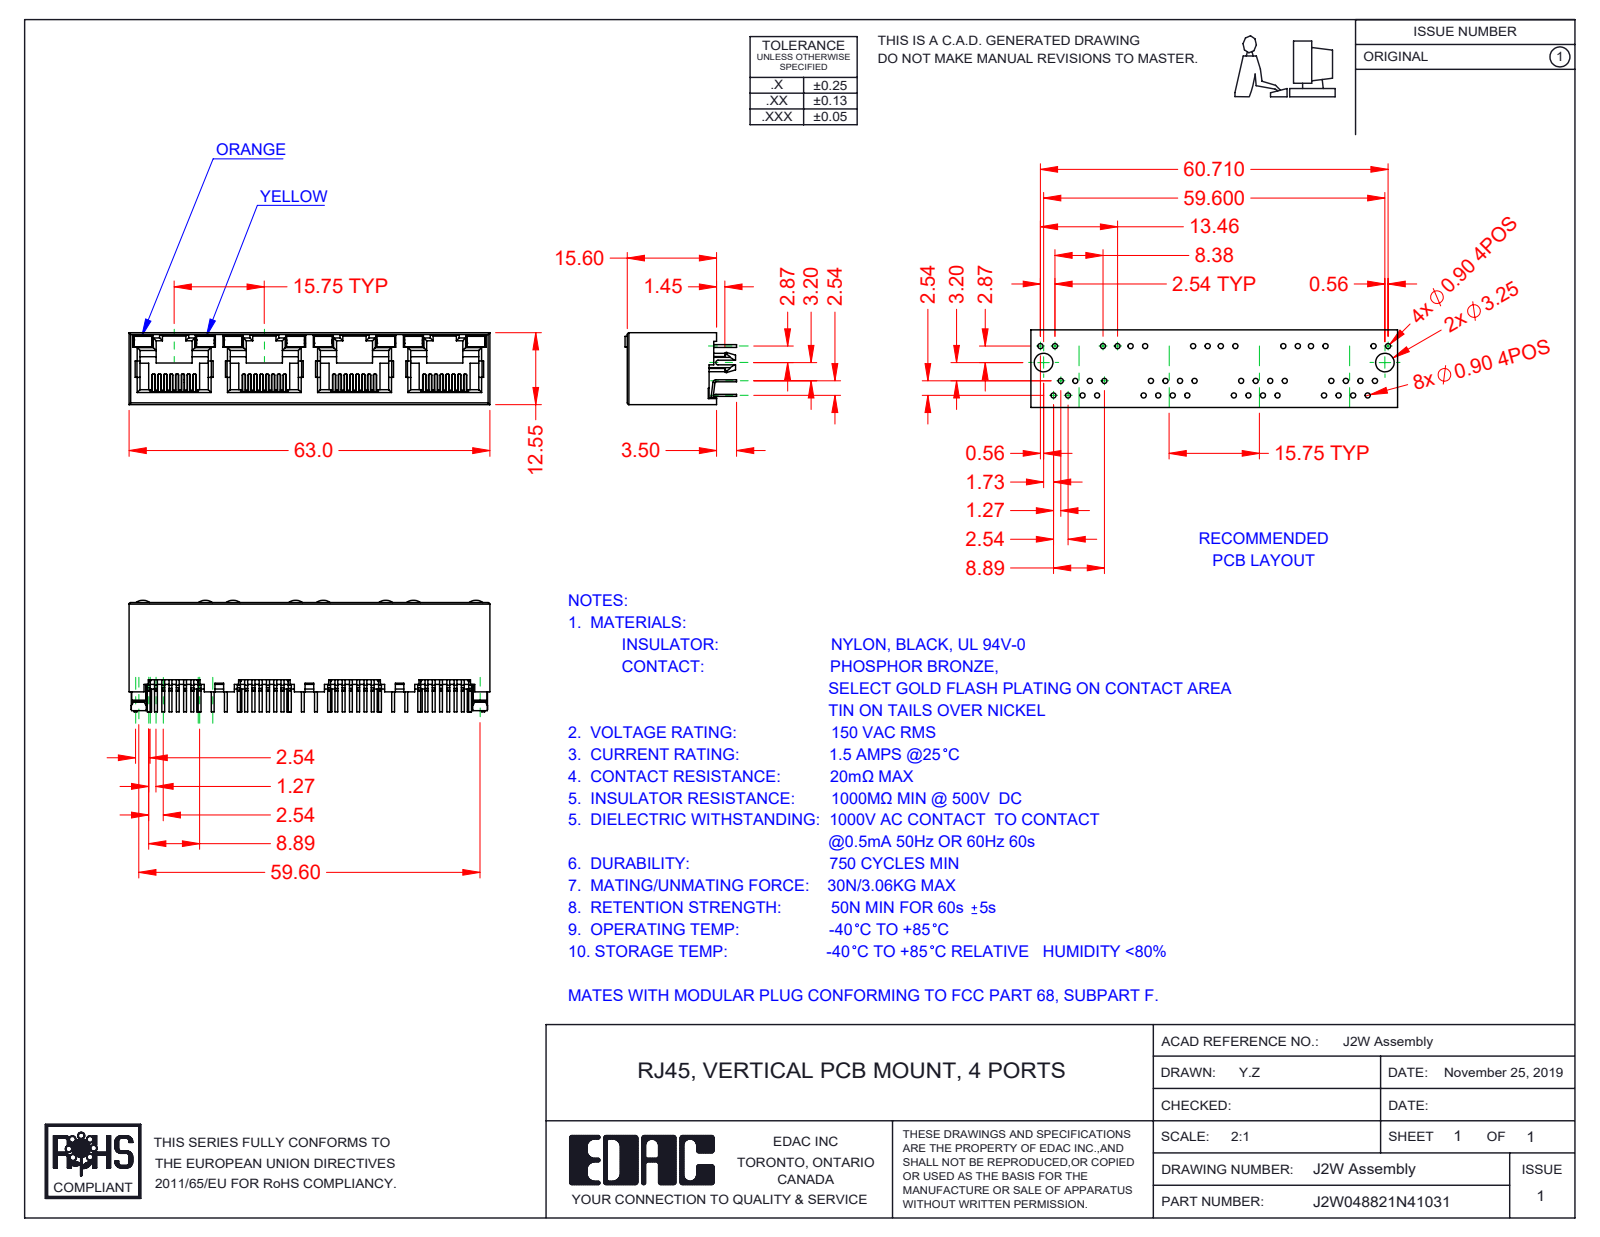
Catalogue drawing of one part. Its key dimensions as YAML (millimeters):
part_name: "2W Contacts; 2W Insulator; J2W048821N41131; 2W LED RH_1-Yellow (+2 more)"
step_written_by: "SolidWorks 2016 (CONFIG_CONTROL_DESIGN)"
units: millimeters
bodies: {solids: 45, faces: 3135, planar: 2600, cylindrical: 477, other: 58}
overall_size: [63, 19.5, 12.55]
volume: 5335
surface_area: 13144
partial_cylinders:
  - {radius: 0.15, count: 64}
  - {radius: 0.2, count: 29}
  - {radius: 0.5, count: 28}
  - {radius: 0.3, count: 14}
  - {radius: 0.45, count: 8}
  - {radius: 2, count: 8}
  - {radius: 0.25, count: 2}
  - {radius: 1.5, count: 2}
face_to_face_distances: [12.55, 11.9, 0.65, 15.75, 0.36, 1.5, 0.78, 0.6, 11.3, 31.5]
